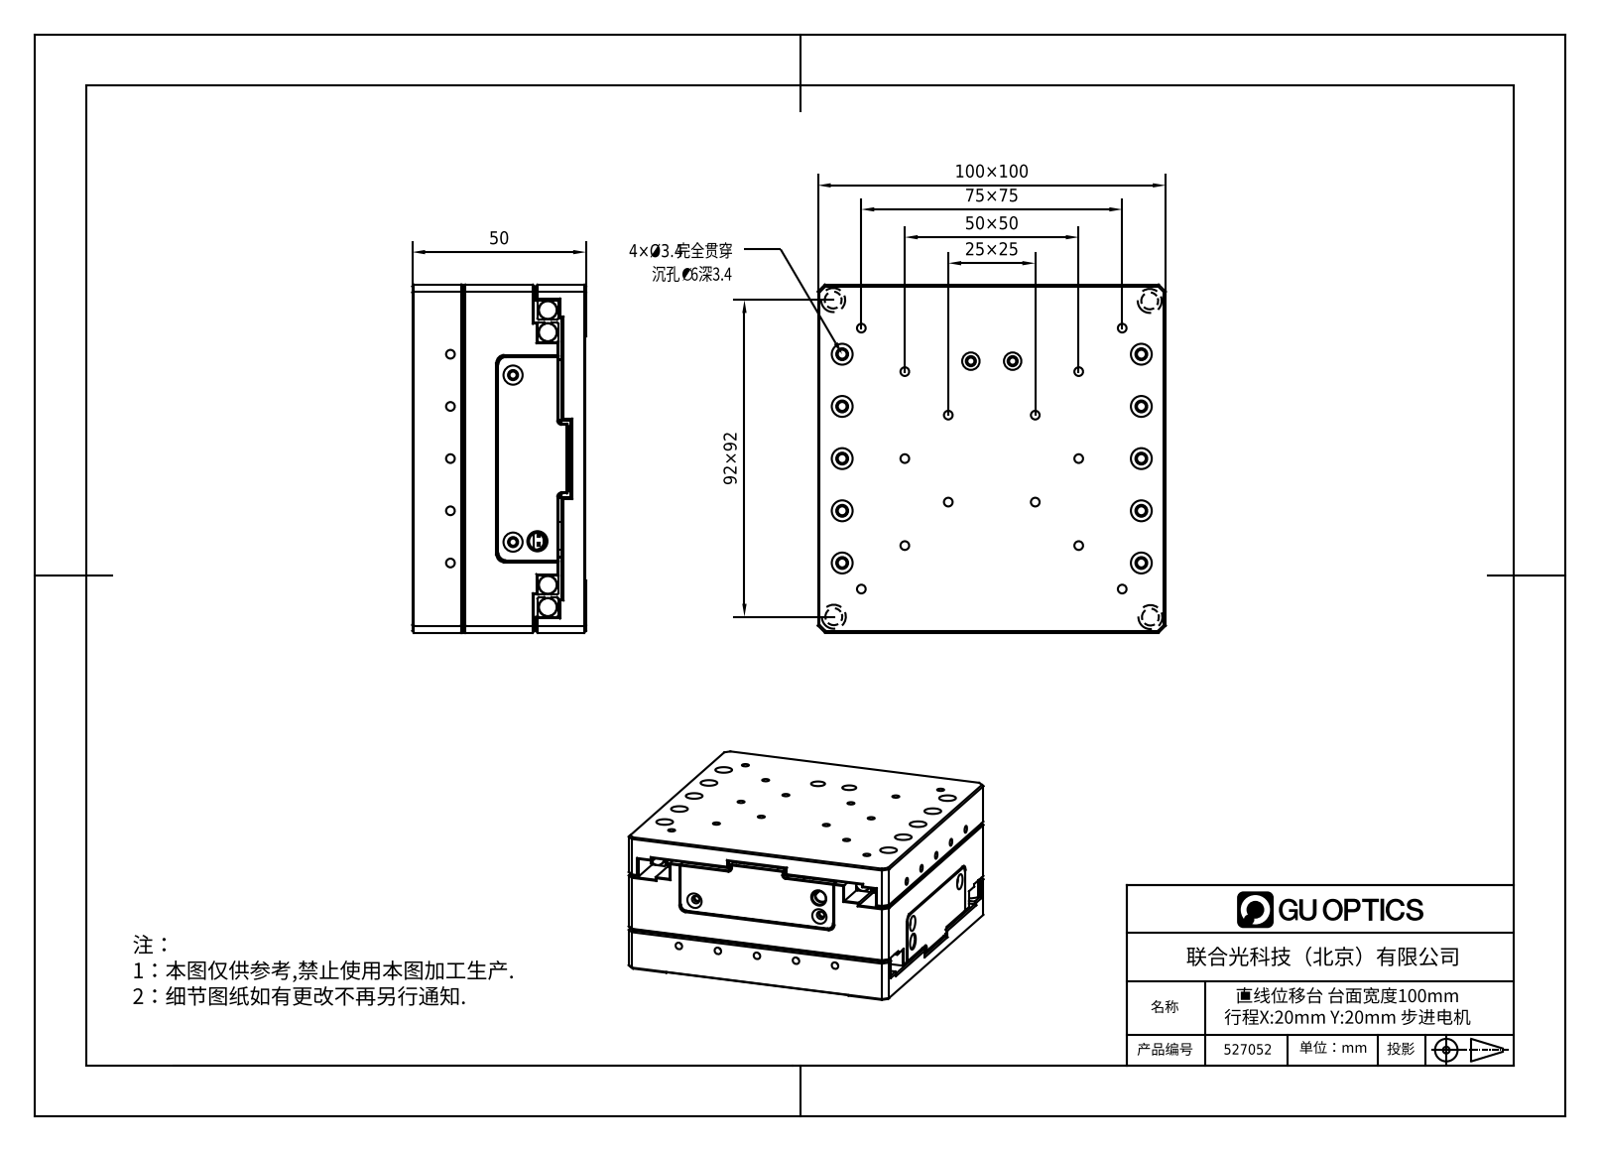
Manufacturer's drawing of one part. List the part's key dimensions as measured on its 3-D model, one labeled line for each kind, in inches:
Part name (STEP PRODUCT): FMSXY100-20-A
STEP written by: SolidWorks 2017 (CONFIG_CONTROL_DESIGN)
Units: inches
Bodies: 0 solids, 3454 faces (1741 planar, 1097 cylindrical, 616 other)
Overall size (bounding box): 3.937 × 3.937 × 1.969
Round holes (diameter × count): ⌀0.063 ×44, ⌀0.1 ×40, ⌀0.173 ×40, ⌀0.081 ×32, ⌀0.236 ×26, ⌀0.098 ×24, ⌀0.114 ×24, ⌀0.134 ×24, ⌀0.049 ×20, ⌀0.02 ×12, ⌀0.197 ×12, ⌀0.087 ×8
Round bosses / shafts (diameter × count): ⌀0.138 ×8, ⌀0.079 ×8, ⌀0.346 ×2, ⌀0.217 ×2, ⌀0.472 ×1, ⌀0.177 ×1, ⌀0.157 ×1, ⌀0.098 ×1
Partial cylindrical surfaces — rounded edges, fillets, slot ends (radius × count): R0.079 ×56, R0.039 ×48, R0.012 ×16, R0.098 ×16, R0.043 ×8, R0.059 ×8, R0.071 ×8, R0.085 ×8
Main face-to-face distances: 0.276, 0.039, 0.315, 0.827, 1.102, 0.118, 1.417, 0.689, 0.551, 0.059
Hole centre spacings: 0.591, 1.181, 2.896, 1.772, 3.071, 2.835, 0.059, 0.12
